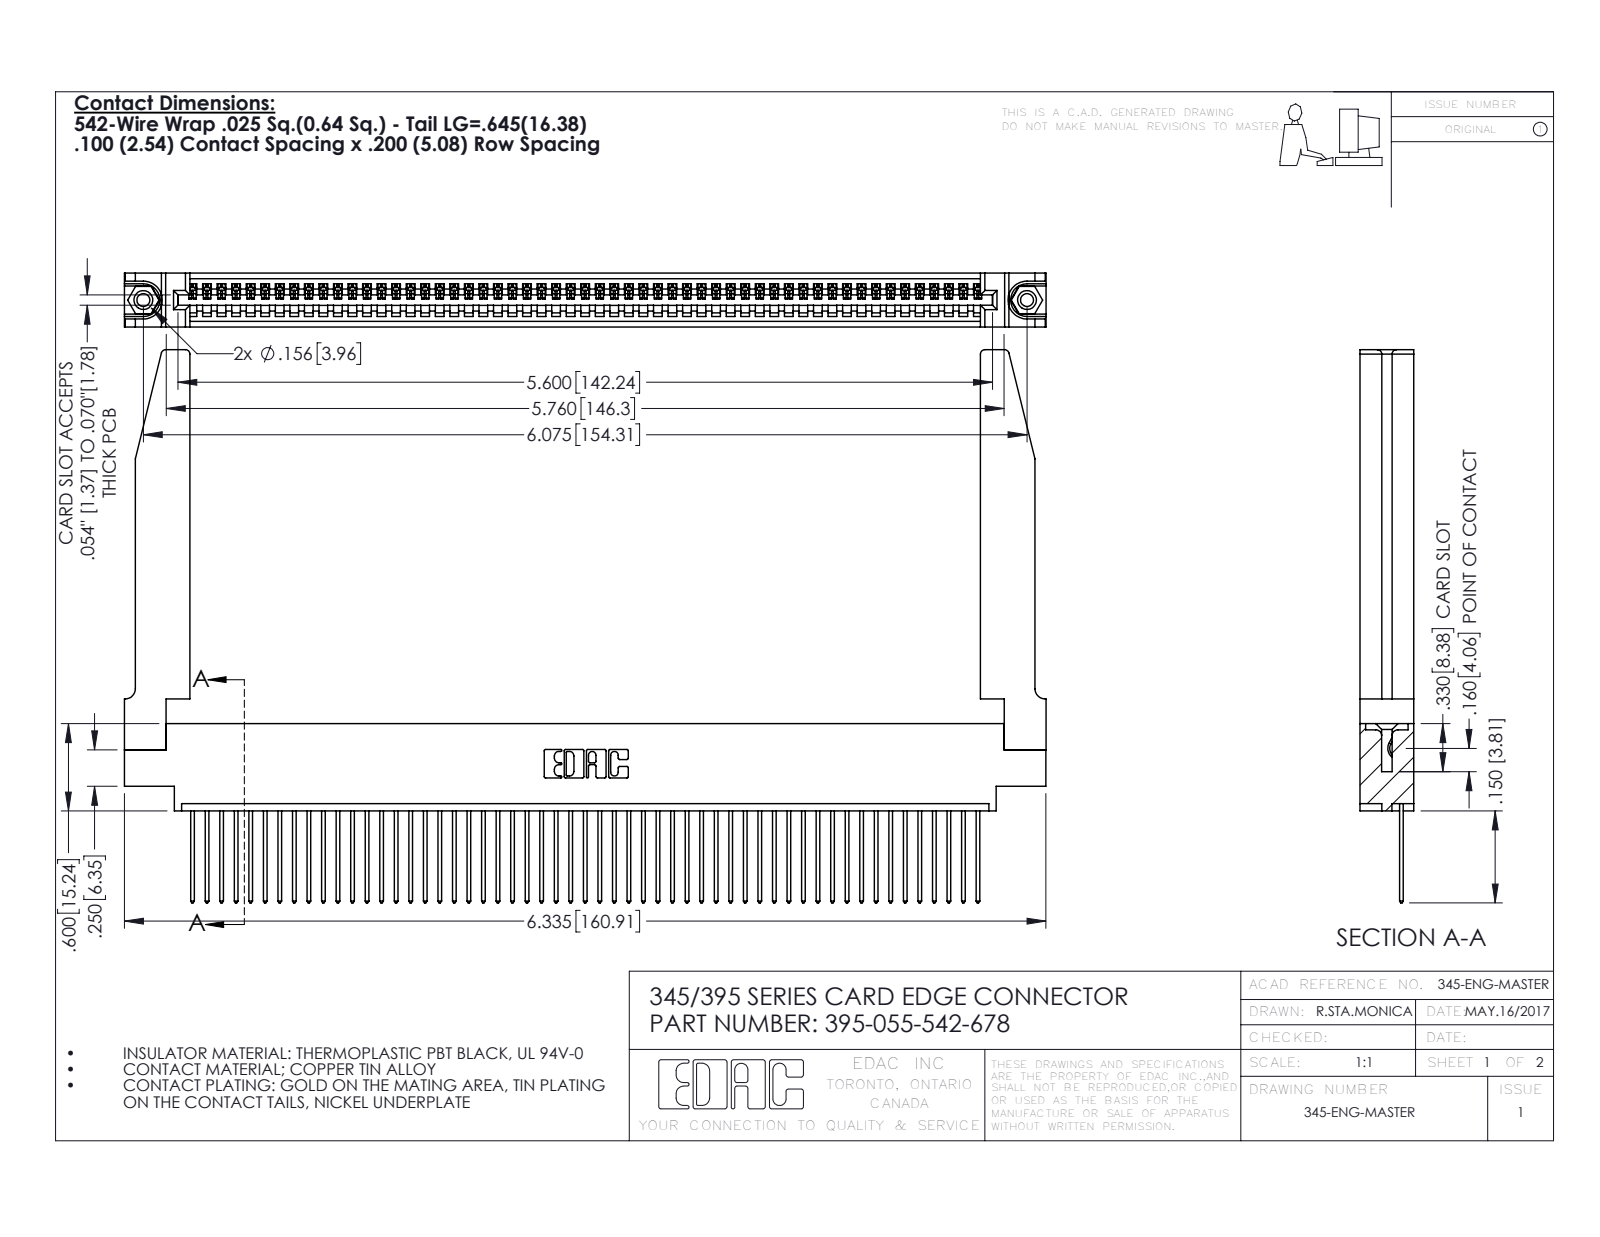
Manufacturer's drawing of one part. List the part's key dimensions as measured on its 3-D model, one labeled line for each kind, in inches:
Part name (STEP PRODUCT): 345-220-078_345-220-078; 345-250-001_345-250-001-102; 395-055-542-678; 345-292-001_345-293-142 (+1 more)
STEP written by: SolidWorks 2016 (CONFIG_CONTROL_DESIGN)
Units: inches
Bodies: 60 solids, 3554 faces (2426 planar, 1076 cylindrical, 52 other)
Overall size (bounding box): 6.336 × 3.802 × 0.37
Volume: 1.414 in³ · Surface area: 44 in²
Round holes (diameter × count): ⌀0.089 ×2, ⌀0.125 ×2, ⌀0.156 ×2, ⌀0.064 ×1
Round bosses / shafts (diameter × count): ⌀0.155 ×2
Partial cylindrical surfaces — rounded edges, fillets, slot ends (radius × count): R0.006 ×110, R0.01 ×110, R0.01 ×22, R0.03 ×8, R0.007 ×6, R0.031 ×6, R0.026 ×3, R0.031 ×2
Main face-to-face distances: 0.072, 0.37, 0.298, 0.098, 0.272, 0.025, 0.2, 0.225, 0.148, 0.15
Hole centre spacings: 0.27, 5.839, 6.075
